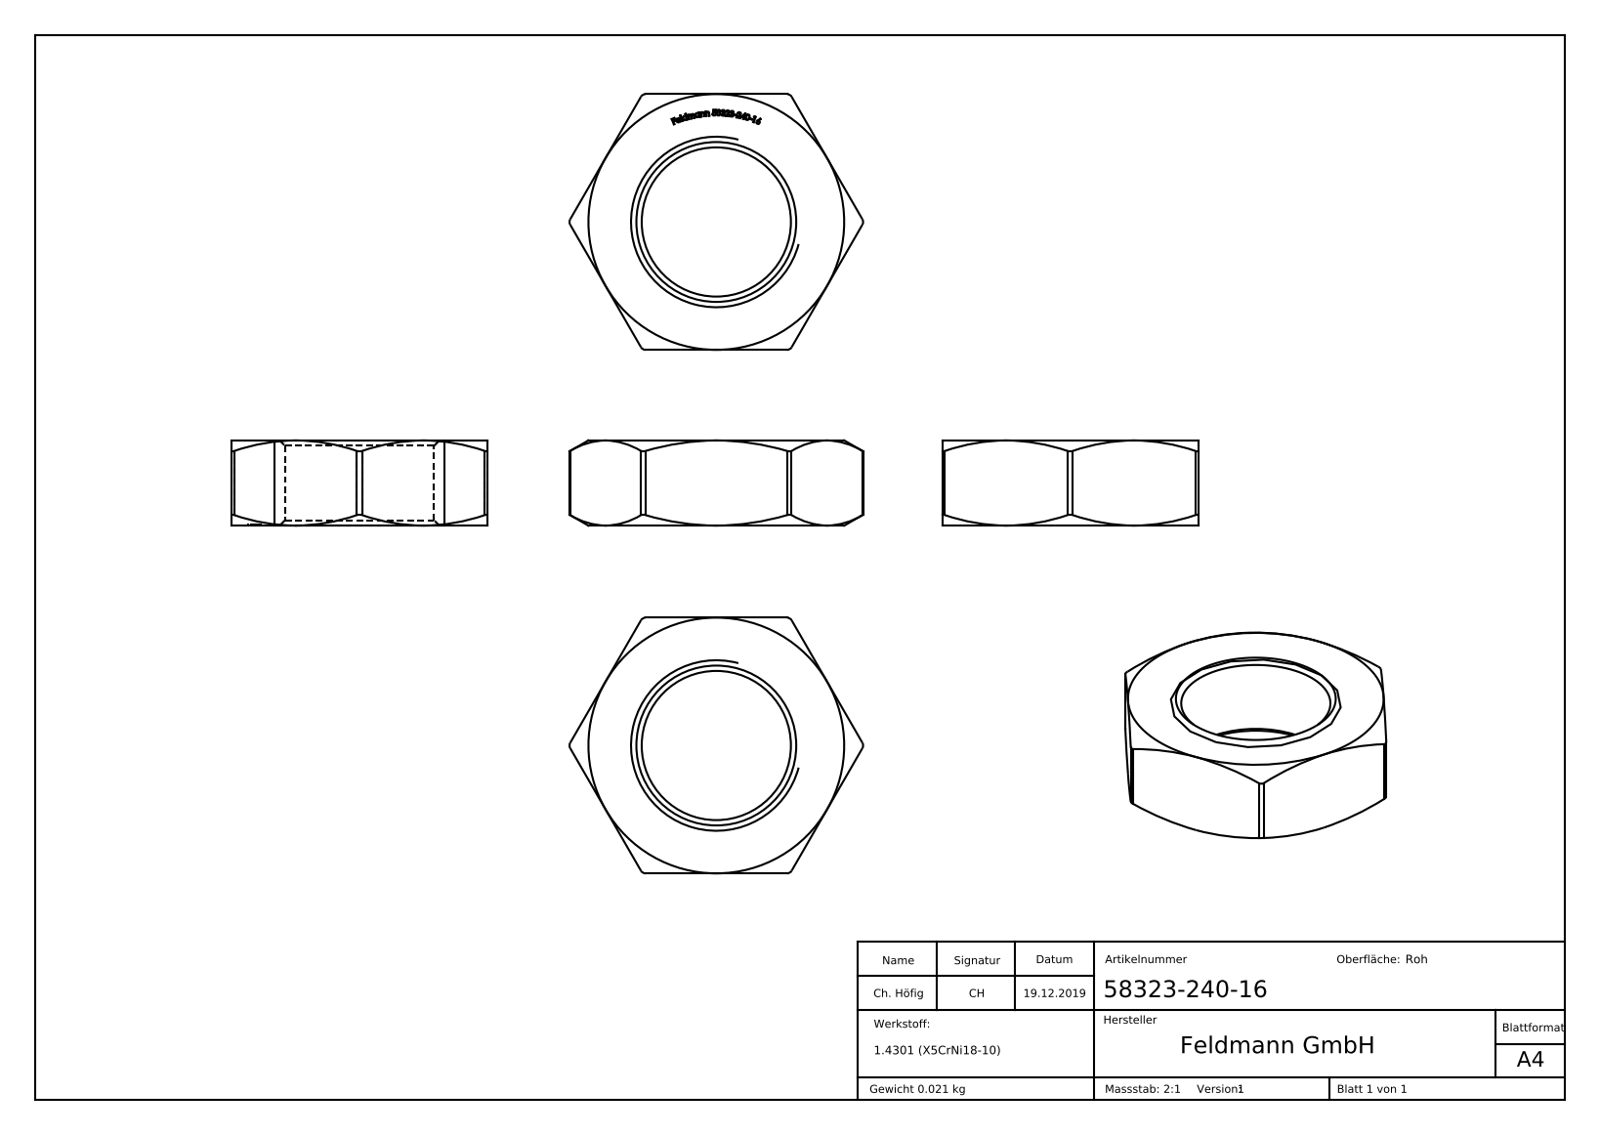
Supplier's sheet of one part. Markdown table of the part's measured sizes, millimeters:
| quantity | value |
| --- | --- |
| part name | 58323-240-16 |
| STEP written by | SolidWorks 2015 (CONFIG_CONTROL_DESIGN) |
| units | millimeters |
| bodies | 1 solid, 296 faces (144 planar, 7 cylindrical, 145 other) |
| overall size | 27.56 × 24 × 22 |
| volume | 2 717 mm³ |
| surface area | 1 637 mm² |
| round holes (diameter × count) | 14 × 1 |
| partial cylindrical surfaces (radius × count) | 0.5 × 6 |
| main face-to-face distances | 24, 8, 7.9, 0.31, 0.34, 0.35, 0.39, 0.36, 0.54, 0.4 |
